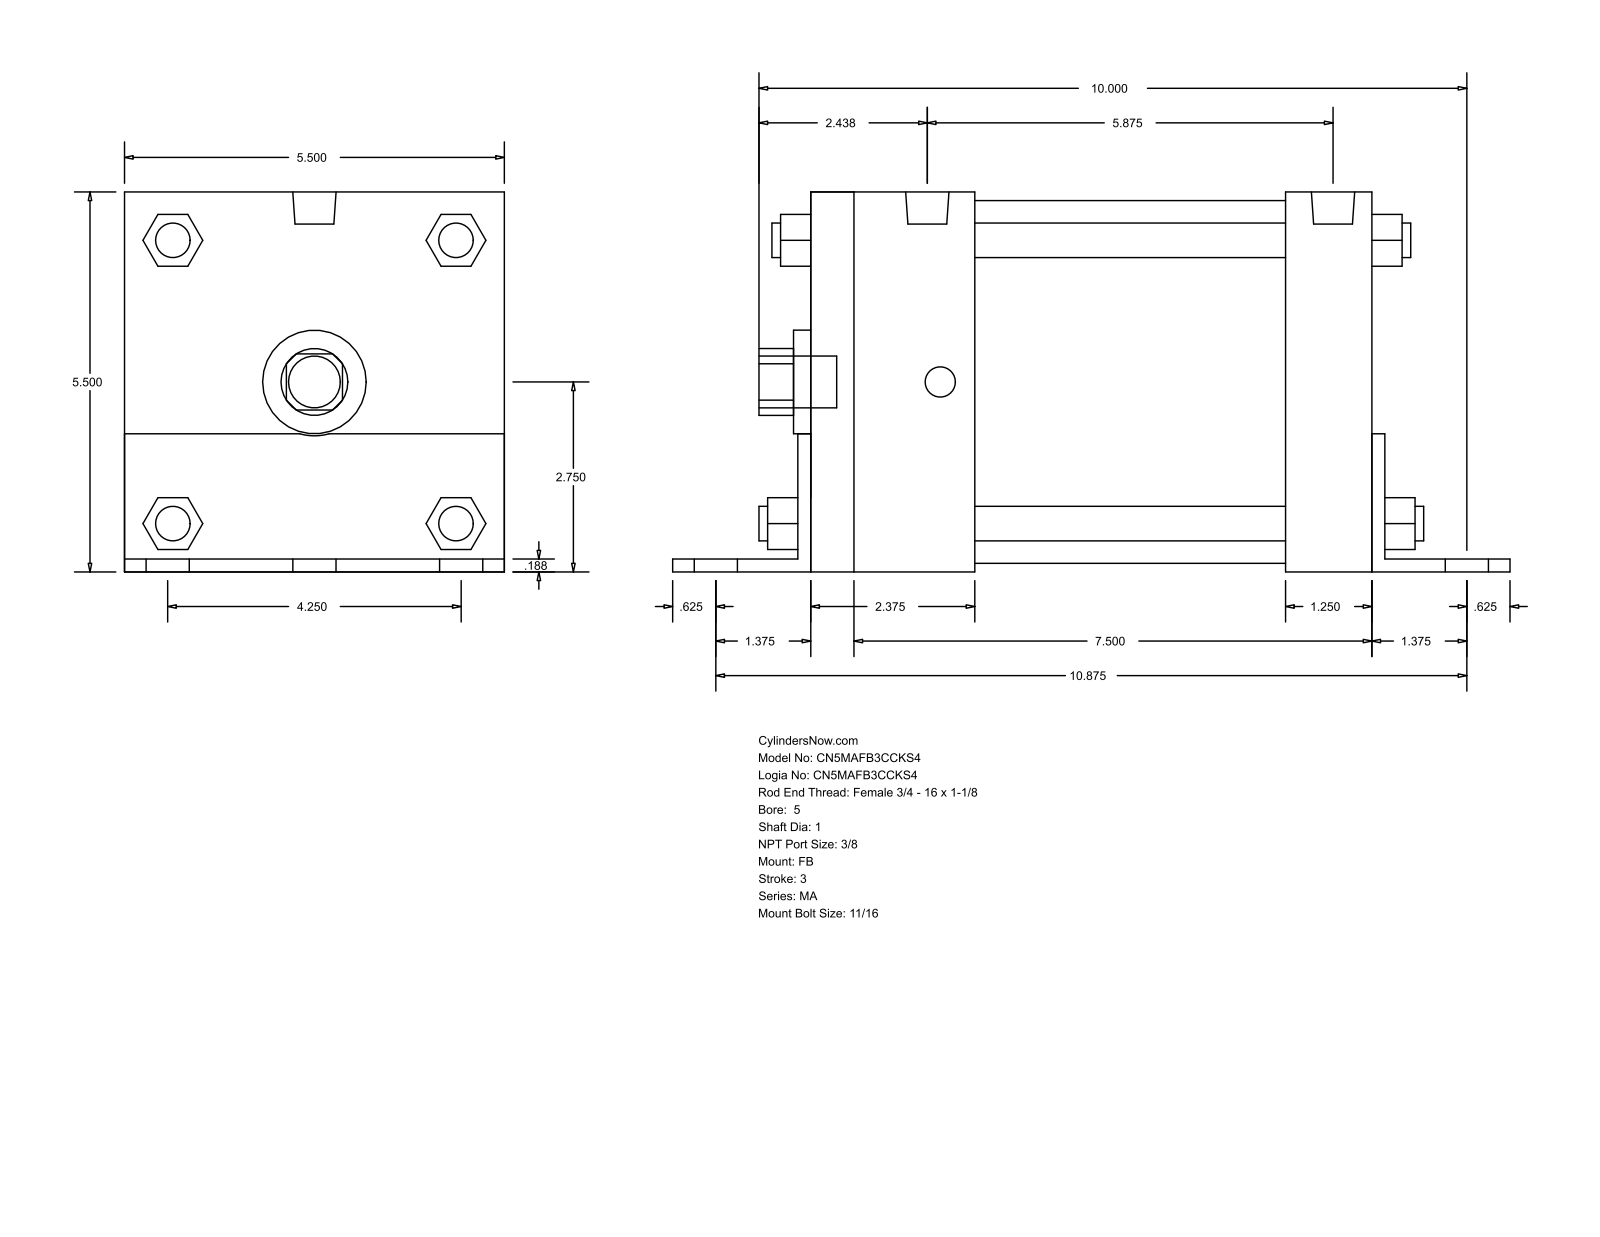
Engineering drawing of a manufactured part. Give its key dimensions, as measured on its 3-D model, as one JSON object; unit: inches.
{"part_name": "MA_FB__0500_1", "step_written_by": "GSSL Pune (CONFIG_CONTROL_DESIGN)", "units": "inches", "bodies": {"solids": 0, "faces": 140, "planar": 105, "cylindrical": 35, "other": 0}, "overall_size": [12.125, 5.502, 5.5], "round_holes": [[1, 1], [1.5, 1], [5.25, 1]], "round_bosses_or_shafts": [[0.687, 6], [0.5, 4], [0.437, 4], [0.627, 2], [0.75, 1]], "partial_cylinders_radius": [[0.484, 1], [0.78, 1]], "face_to_face_distances": [5.5, 0.187, 5.502, 8.313, 0.185, 5.315, 8.125, 8.5, 1.25, 1.437]}
